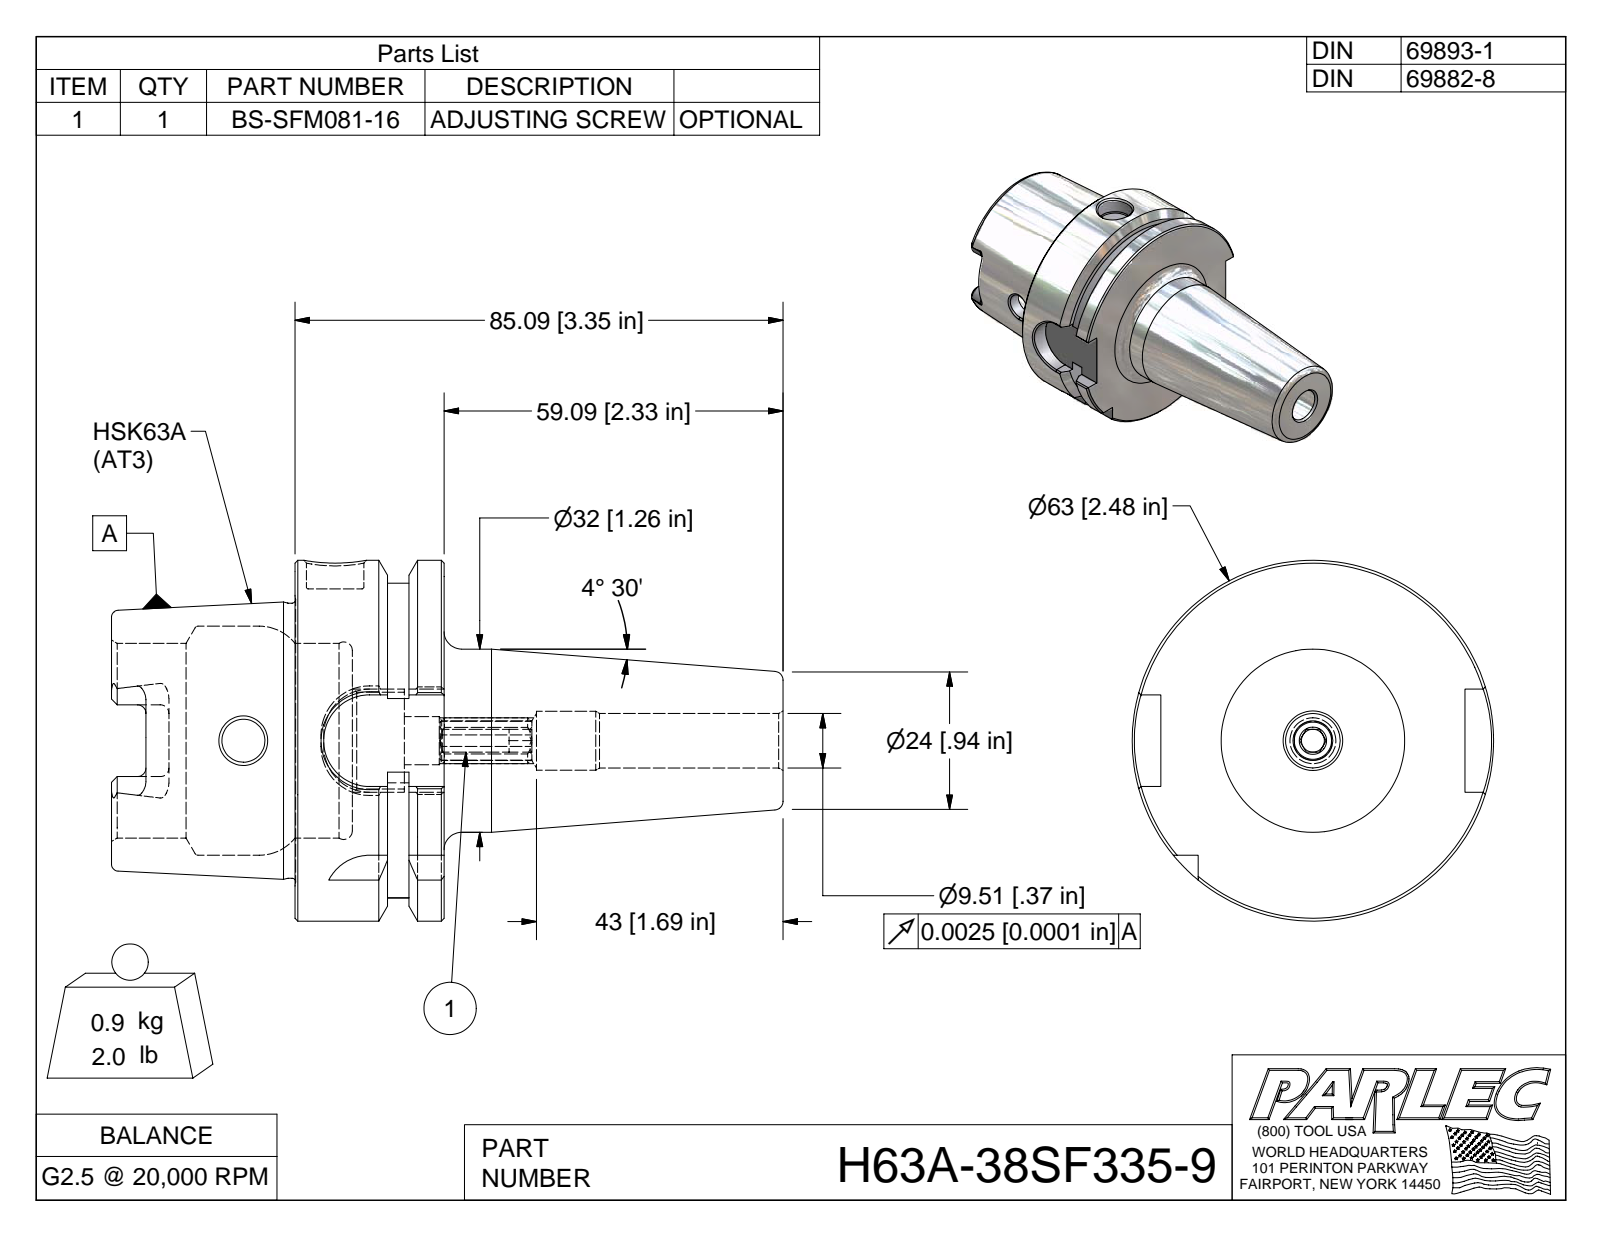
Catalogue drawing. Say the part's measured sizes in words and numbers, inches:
The part is named "H63A-38SF335-9; H63A-38SF335-9-1; BS-SFM081-16". Its 3-D file was written by "Autodesk Inventor 2009 (AUTOMOTIVE_DESIGN)". It is 2 solids with 157 faces: 58 planar, 35 cylindrical and 64 other. Overall it measures 4.61 by 2.48 by 2.48 inches. Its volume is 7.124 cubic inches and its surface area 45.59 square inches. Round holes: 1 of diameter 0.295, 1 of diameter 0.374, 1 of diameter 0.394, 1 of diameter 0.404, 1 of diameter 0.666, 1 of diameter 1.339, 1 of diameter 1.575. Round bosses or shafts: 1 of diameter 2.48, 1 of diameter 1.891, 1 of diameter 1.26. Partial cylindrical surfaces (rounded edges, fillets, slot ends): 6 of radius 0.059, 4 of radius 0.113, 4 of radius 0.315, 1 of radius 0.157, 1 of radius 1.083. The main face-to-face distances are 1.024, 0.241, 0.389, 0.394, 0.63, 1.26, 1.654, 2.283, 1.894, 0.635.
